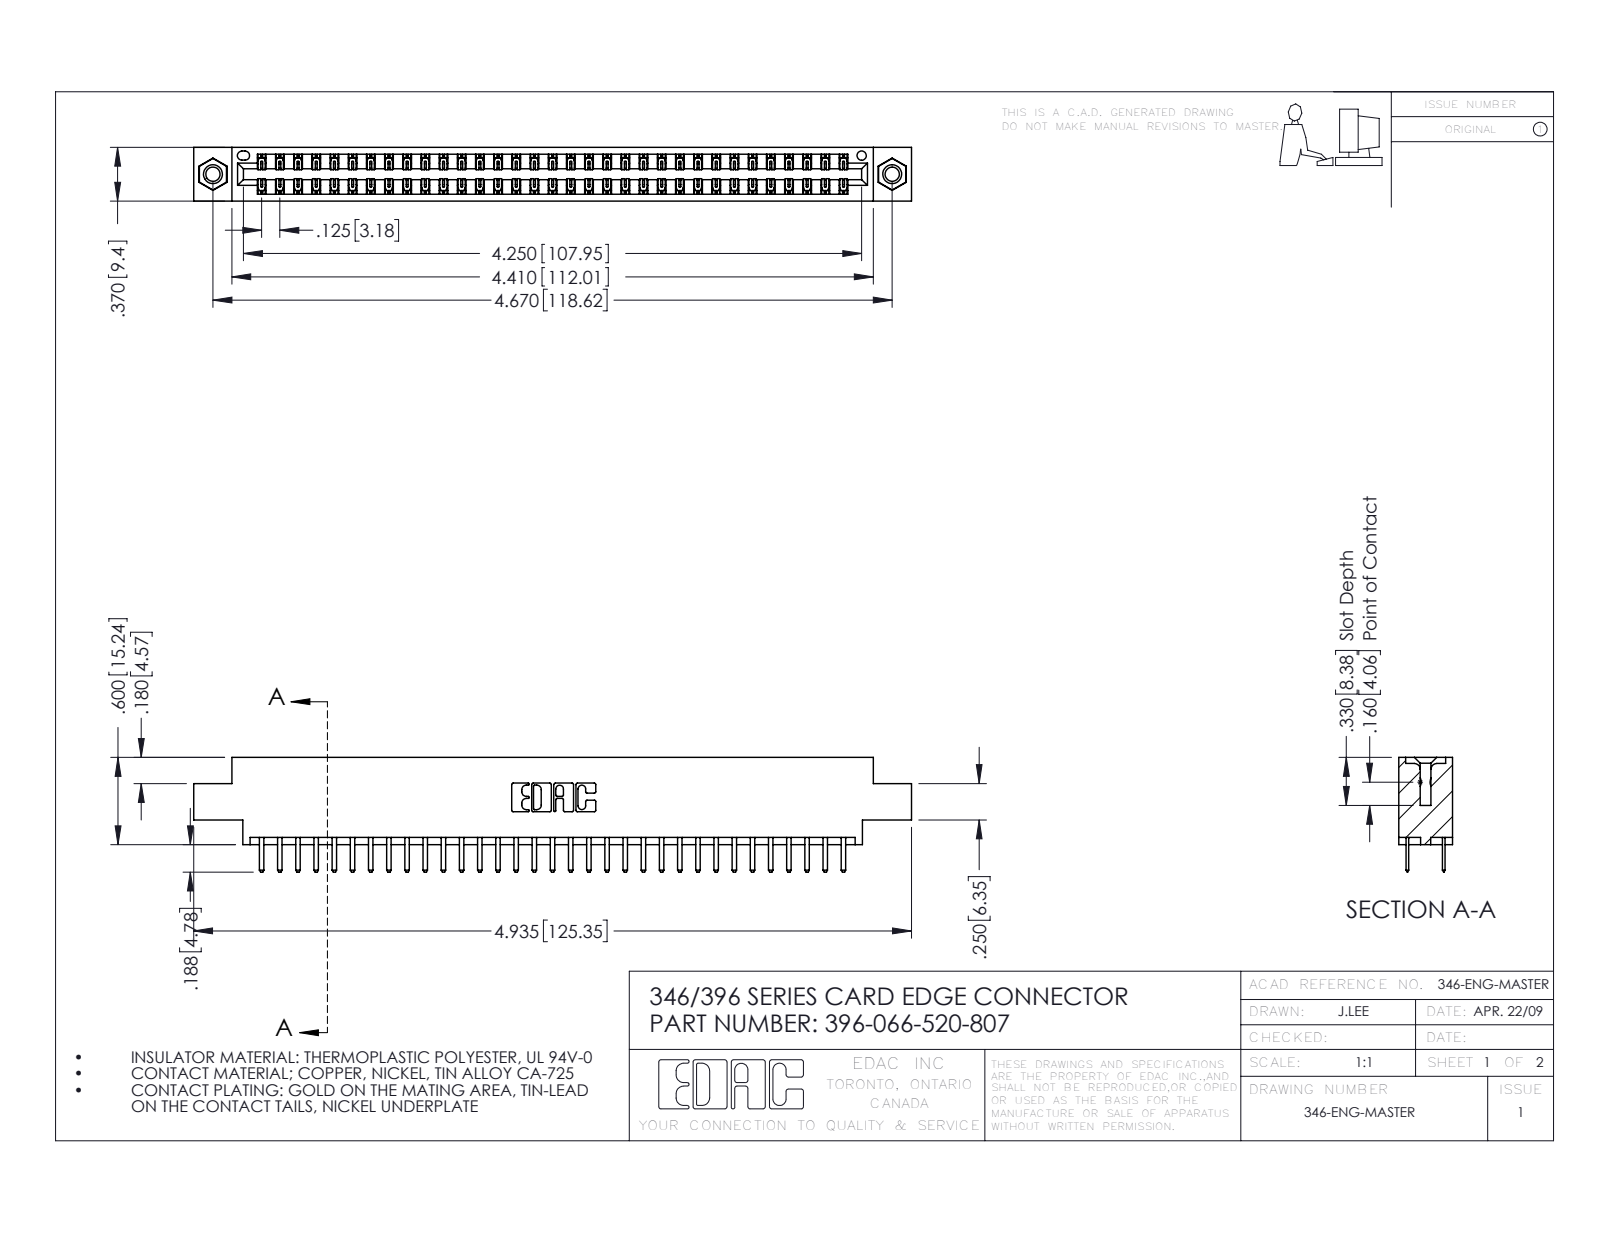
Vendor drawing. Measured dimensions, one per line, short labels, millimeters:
name: 346 Part_0.170 Offset - 0.156 Dia-TI; 345-292-001_345-293-120; 396-066-520-807; 345-250-001_345-250-005-103
written by: SolidWorks 2016 (CONFIG_CONTROL_DESIGN)
unit: mm
bodies: 69 solids, 3882 faces (2554 planar, 1312 cylindrical, 16 other)
size: 125.3 × 20 × 9.4
volume: 12 000 mm³; area: 16 440 mm²
holes: 2× ⌀2.5, 2× ⌀3.2, 2× ⌀4, 1× ⌀1.6
bosses: 2× ⌀3.9
rounds: 99× R0.2, 70× R0.3, 22× R0.3, 6× R0.2, 6× R0.8, 3× R0.7, 2× R0.4, 2× R0.6
face distances: 1.2, 8.2, 9.4, 6.4, 7, 1.8, 7.6, 0.6, 5.6, 3.8
hole spacings: 6.2, 113.3, 118.6
